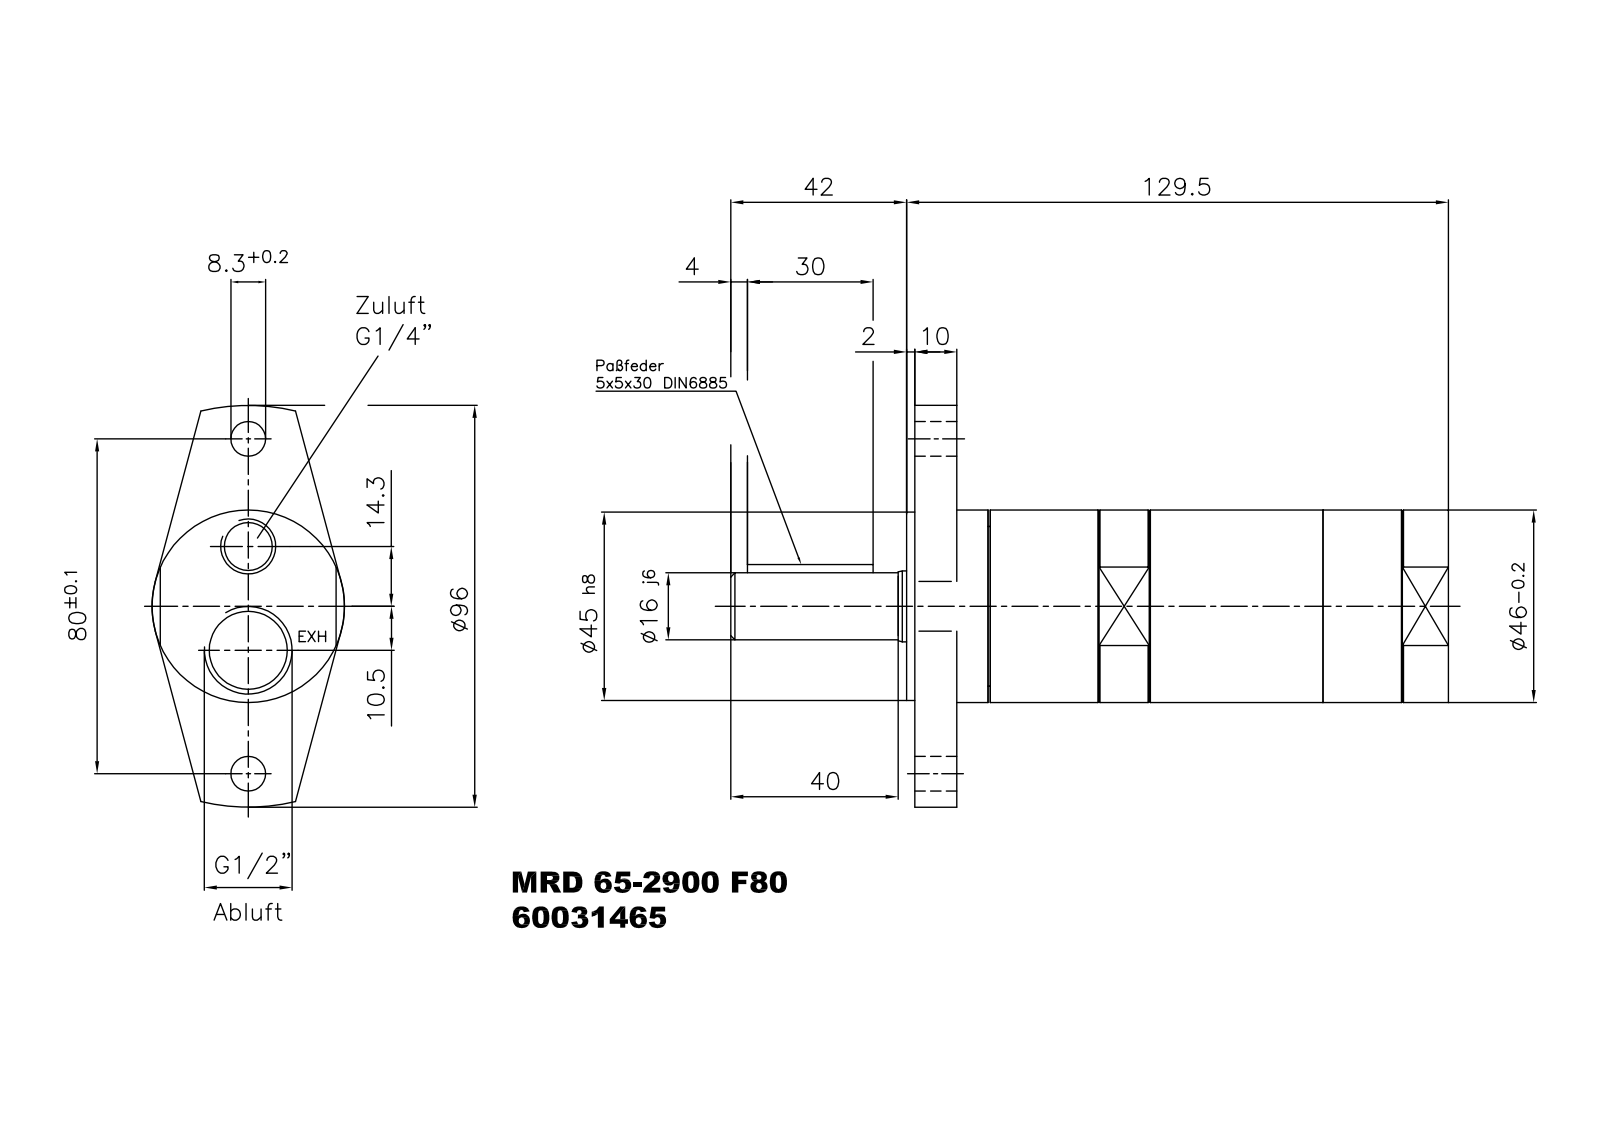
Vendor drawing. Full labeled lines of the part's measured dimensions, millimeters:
Part name (STEP PRODUCT): MRD 65-10500 2900 2300 1300 F80 171,5mm
STEP written by: Autodesk Inventor 2013 (AUTOMOTIVE_DESIGN)
Units: millimetres
Bodies: 2 solids, 146 faces (91 planar, 22 cylindrical, 33 other)
Overall size (bounding box): 177.5 × 96 × 46
Volume: 242 670 mm³ · Surface area: 35 816 mm²
Round holes (diameter × count): ⌀8.3 ×2, ⌀1.6 ×1, ⌀11.45 ×1, ⌀17.5 ×1, ⌀18.63 ×1
Round bosses / shafts (diameter × count): ⌀46 ×1, ⌀45 ×1, ⌀40 ×1, ⌀16.95 ×1, ⌀16 ×1
Partial cylindrical surfaces — rounded edges, fillets, slot ends (radius × count): R2.5 ×2, R48 ×1
Main face-to-face distances: 103.5, 10, 93.5, 12, 2, 105.5, 123.5, 135.5, 133.5, 30
Hole centre spacings: 40, 10.5, 14.3, 24.8, 25.7, 29.5, 50.5, 54.3
